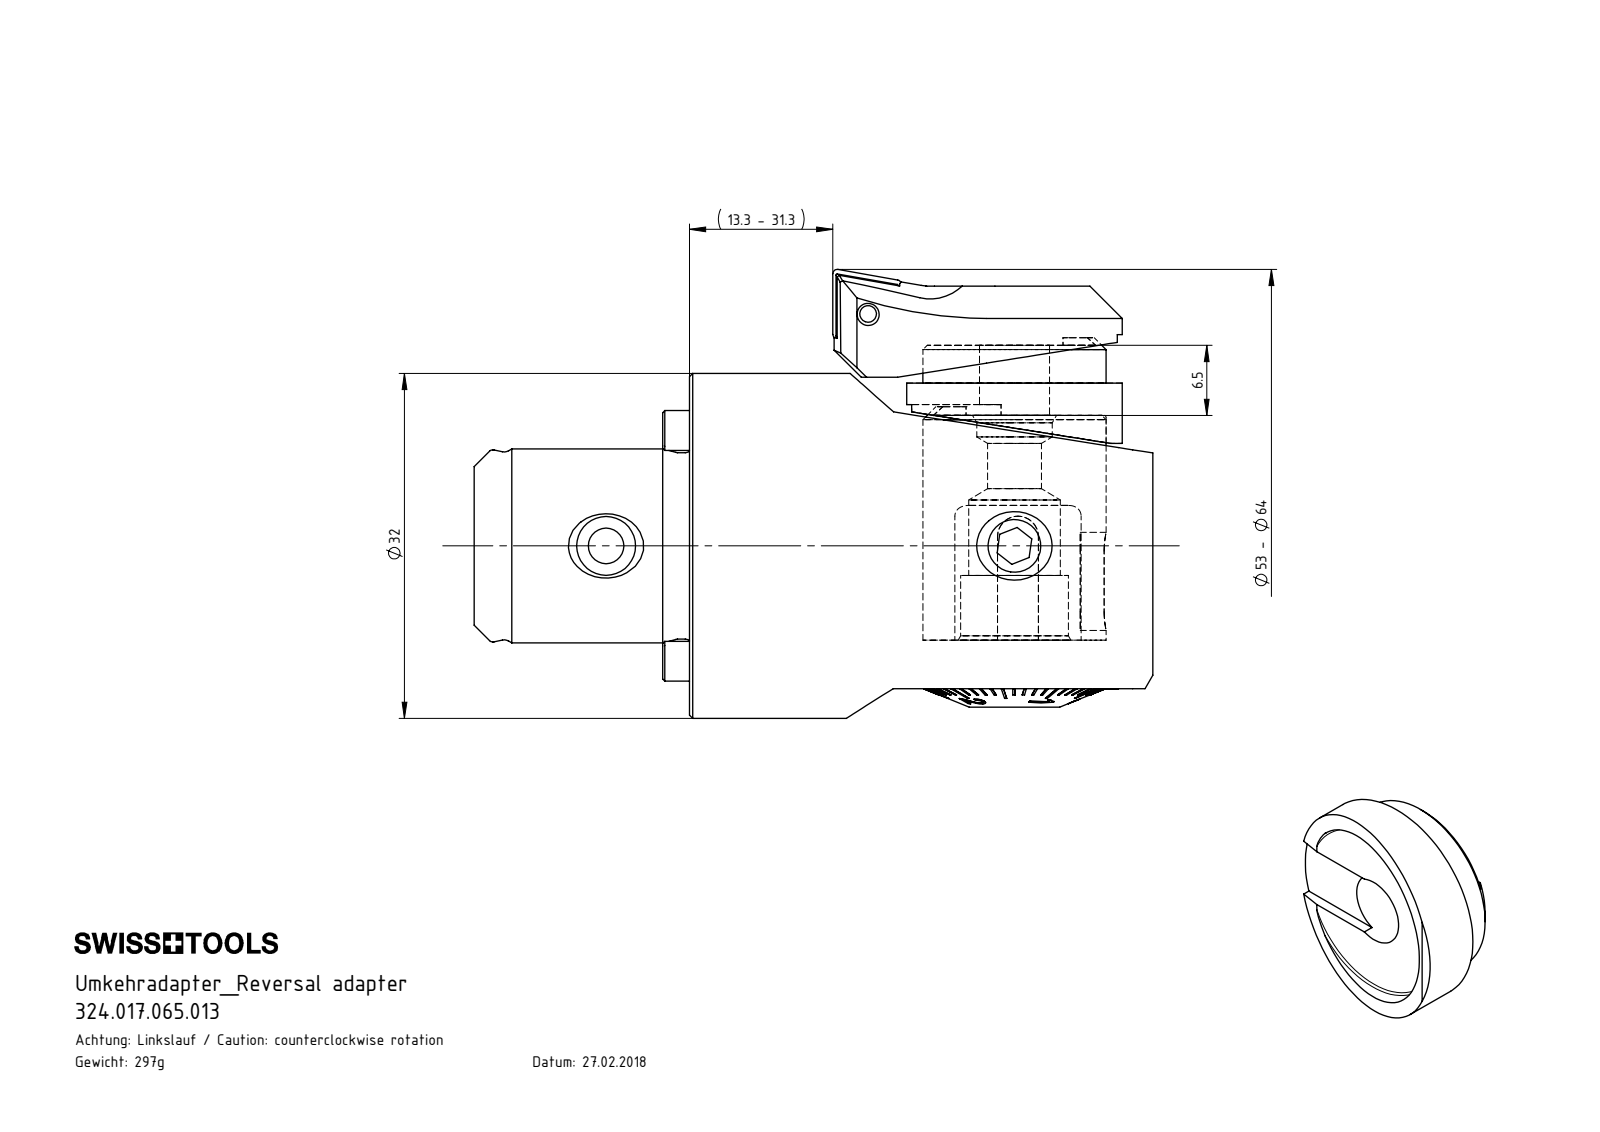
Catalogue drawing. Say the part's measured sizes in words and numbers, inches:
The part is named "324.017.065.013; F32-U00.001.006_B". Its 3-D file was written by "SolidWorks 2017 (CONFIG_CONTROL_DESIGN)". It is 1 solid with 28 faces: 12 planar, 11 cylindrical and 5 other. Overall it measures 0.787 by 0.787 by 0.386 inches. Its volume is 0.097 cubic inches and its surface area 1.869 square inches. Round holes: 1 of diameter 0.256, 1 of diameter 0.669. Round bosses or shafts: 1 of diameter 0.787. Partial cylindrical surfaces (rounded edges, fillets, slot ends): 2 of radius 0.02. The main face-to-face distances are 0.256, 0.138, 0.118, 0.217, 0.079, 0.039, 0.028, 0.165, 0.244, 0.283.
